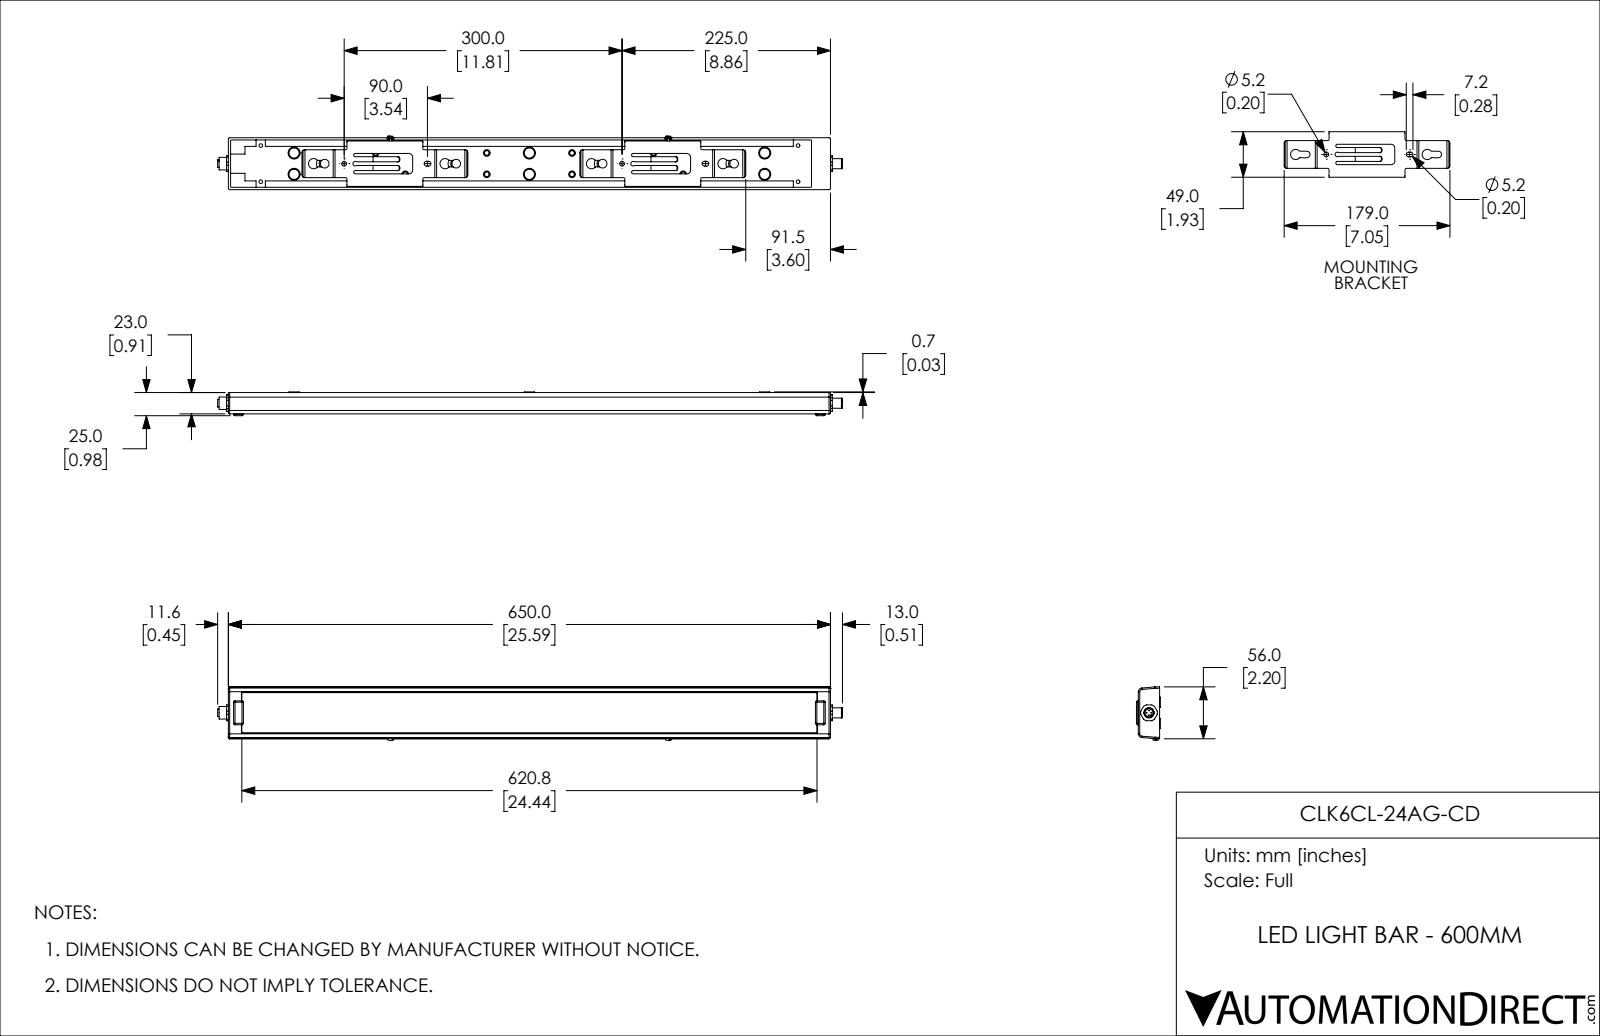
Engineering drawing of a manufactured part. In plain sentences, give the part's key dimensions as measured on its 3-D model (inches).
The part is named "CLK6CL-24AG-CD". Its 3-D file was written by "SolidWorks 2018 (AUTOMOTIVE_DESIGN)". It is 7 solids with 488 faces: 211 planar, 174 cylindrical and 103 other. Overall it measures 26.557 by 2.268 by 1.012 inches. Its volume is 36.14 cubic inches and its surface area 273.1 square inches. Round holes: 5 of diameter 0.031, 4 of diameter 0.157, 2 of diameter 0.118, 2 of diameter 0.205, 1 of diameter 0.335, 1 of diameter 0.472. Round bosses or shafts: 6 of diameter 0.512, 6 of diameter 0.433, 4 of diameter 0.37, 4 of diameter 0.256, 2 of diameter 0.118, 1 of diameter 0.531, 1 of diameter 0.429, 1 of diameter 0.421. Partial cylindrical surfaces (rounded edges, fillets, slot ends): 20 of radius 0.059, 8 of radius 0.079, 4 of radius 0.102, 4 of radius 0.138, 4 of radius 0.217, 2 of radius 0.157, 1 of radius 0.024, 1 of radius 0.354. The main face-to-face distances are 0.697, 0.059, 0.269, 1.739, 0.138, 2.008, 0.404, 0.293, 0.894, 0.197. The hole center spacings are 0.098, 0.139, 0.197, 1.535, 3.626, 7.519, 11.811, 15.374.
